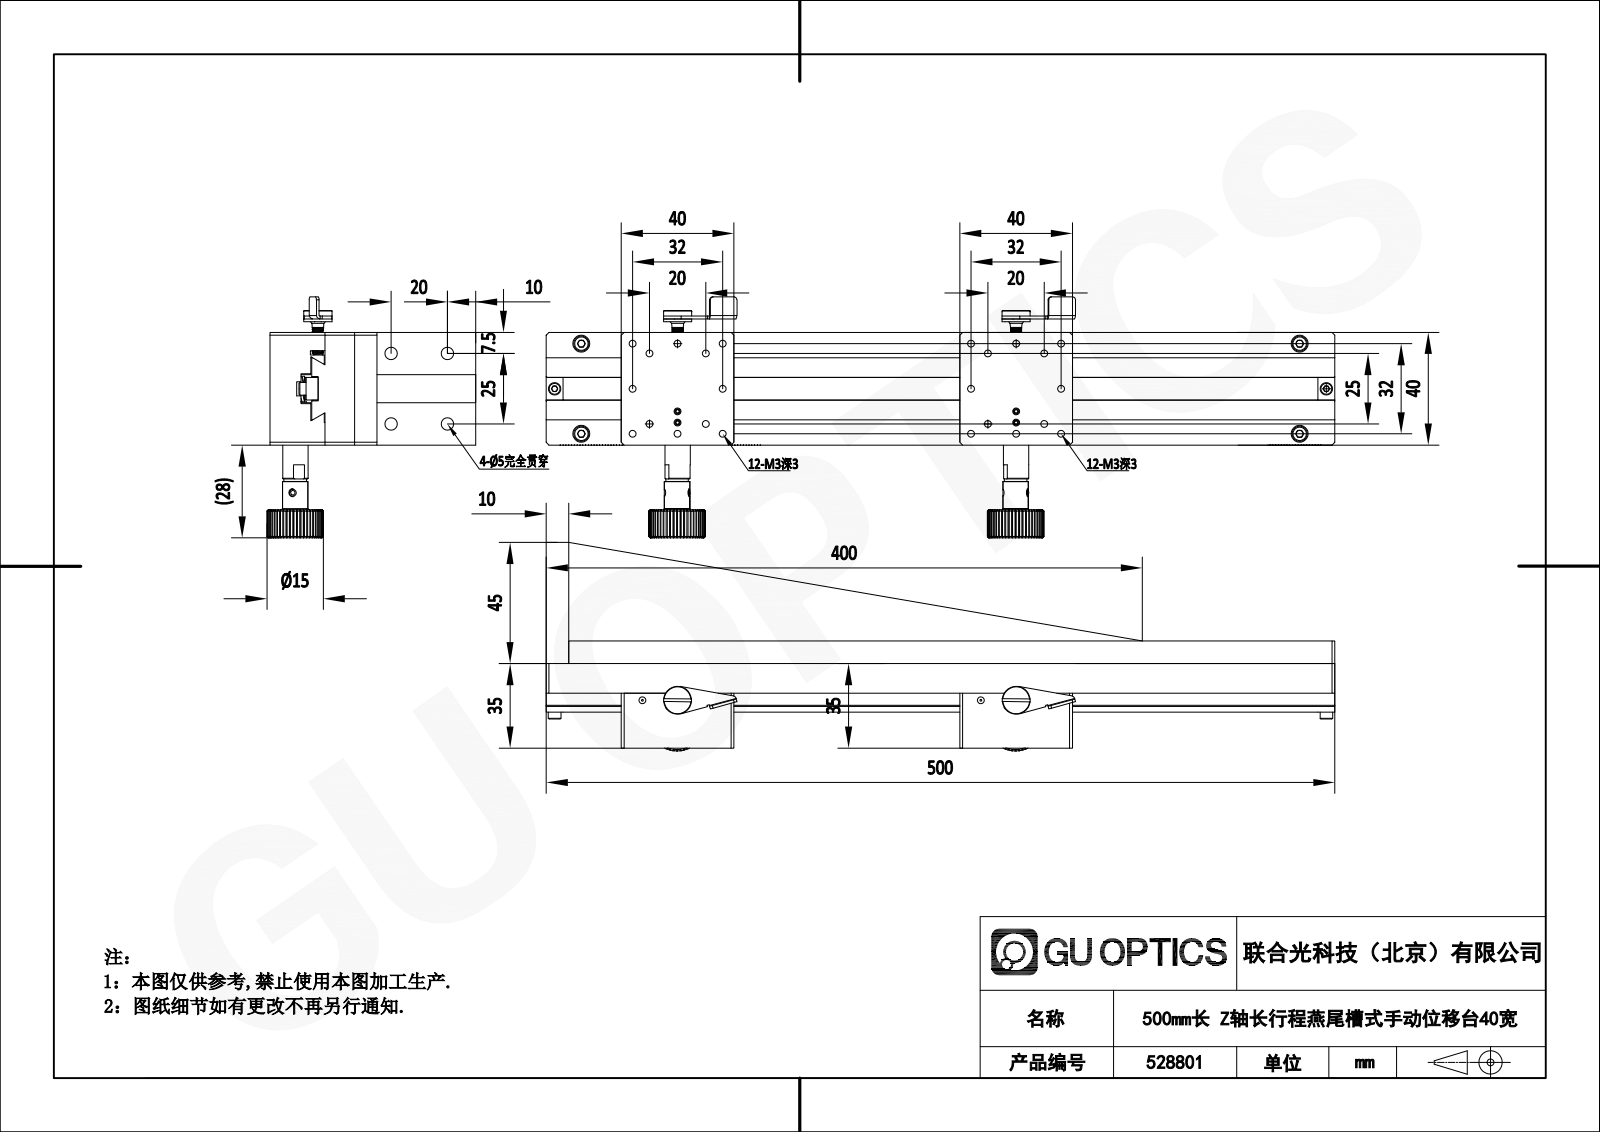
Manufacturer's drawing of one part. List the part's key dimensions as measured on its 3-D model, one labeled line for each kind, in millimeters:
Part name (STEP PRODUCT): 528801
STEP written by: SolidWorks 2020 (CONFIG_CONTROL_DESIGN)
Units: millimetres
Bodies: 55 solids, 2272 faces (1126 planar, 503 cylindrical, 643 other)
Overall size (bounding box): 500 × 85.87 × 80
Volume: 585 764 mm³ · Surface area: 179 409 mm²
Round holes (diameter × count): ⌀2.5 ×50, ⌀3.3 ×24, ⌀6 ×18, ⌀4.5 ×10, ⌀2.05 ×9, ⌀2.9 ×9, ⌀5 ×7, ⌀8 ×6, ⌀4 ×2, ⌀4.1 ×2
Round bosses / shafts (diameter × count): ⌀3 ×12, ⌀2.5 ×9, ⌀5.5 ×8, ⌀4.5 ×7, ⌀4 ×6, ⌀9 ×4, ⌀7 ×4, ⌀10 ×2
Partial cylindrical surfaces — rounded edges, fillets, slot ends (radius × count): R1.05 ×16, R1 ×6, R2.5 ×4, R0.2 ×2, R1.2 ×2, R10 ×2
Main face-to-face distances: 10, 15, 25, 40, 20.5, 10.5, 22.9, 12.9, 2.4, 4.7
Hole centre spacings: 16, 12.5, 32, 35.78, 20, 25, 50, 59.36
